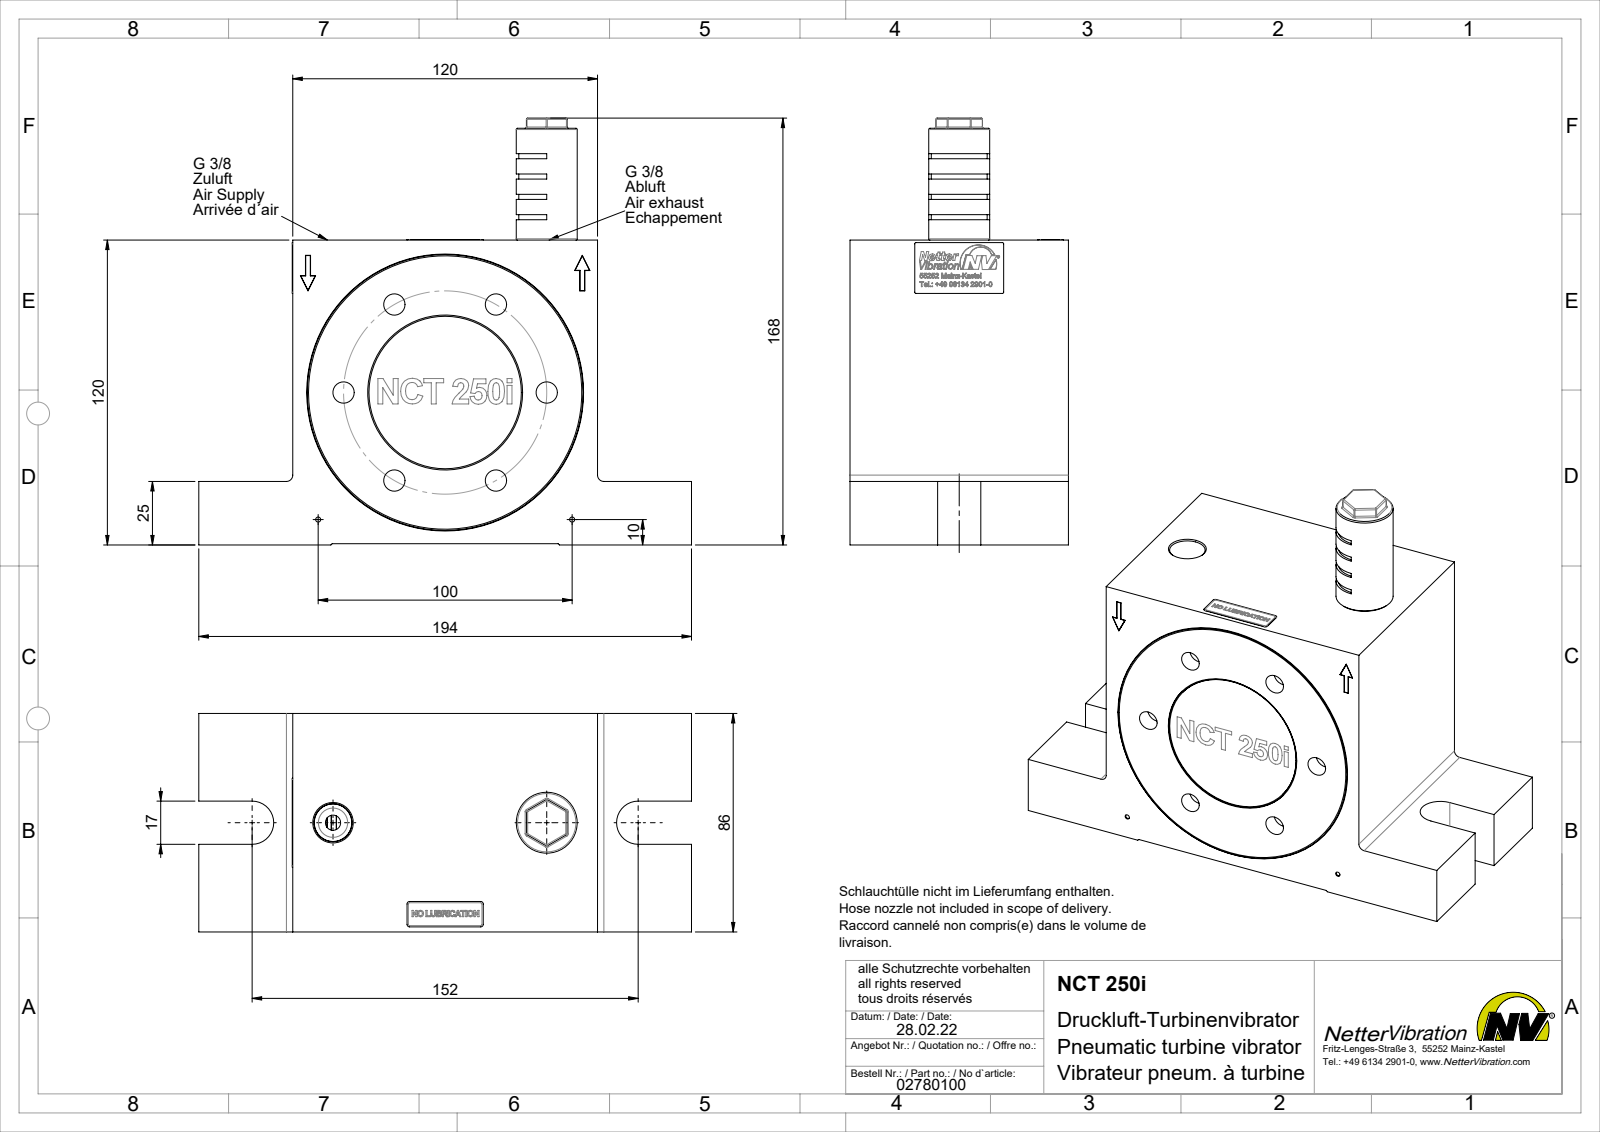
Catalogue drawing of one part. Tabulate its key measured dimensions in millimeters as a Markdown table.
| quantity | value |
| --- | --- |
| part name | NCT 250i Turbinenvibrator #02780100 |
| STEP written by | SolidWorks 2015 (AUTOMOTIVE_DESIGN) |
| units | millimeters |
| bodies | 6 solids, 341 faces (211 planar, 77 cylindrical, 53 other) |
| overall size | 194 × 168 × 86.25 |
| volume | 1 487 000 mm³ |
| surface area | 132 296 mm² |
| round holes (diameter × count) | 8.4 × 6, 2 × 2, 15 × 2, 61 × 1, 106.5 × 1 |
| round bosses / shafts (diameter × count) | 109 × 1, 106.47 × 1, 103.87 × 1, 60 × 1, 24 × 1, 16.66 × 1 |
| partial cylindrical surfaces (radius × count) | 0.5 × 22, 1 × 4, 2.5 × 2, 8.5 × 2, 11 × 1 |
| main face-to-face distances | 120, 0.5, 76, 65.25, 10.75, 119.5, 10, 86, 20.75, 24.5 |
| hole center spacings | 40, 69.28, 80, 32.45, 48.05, 68.62, 71.08, 86.98 |
